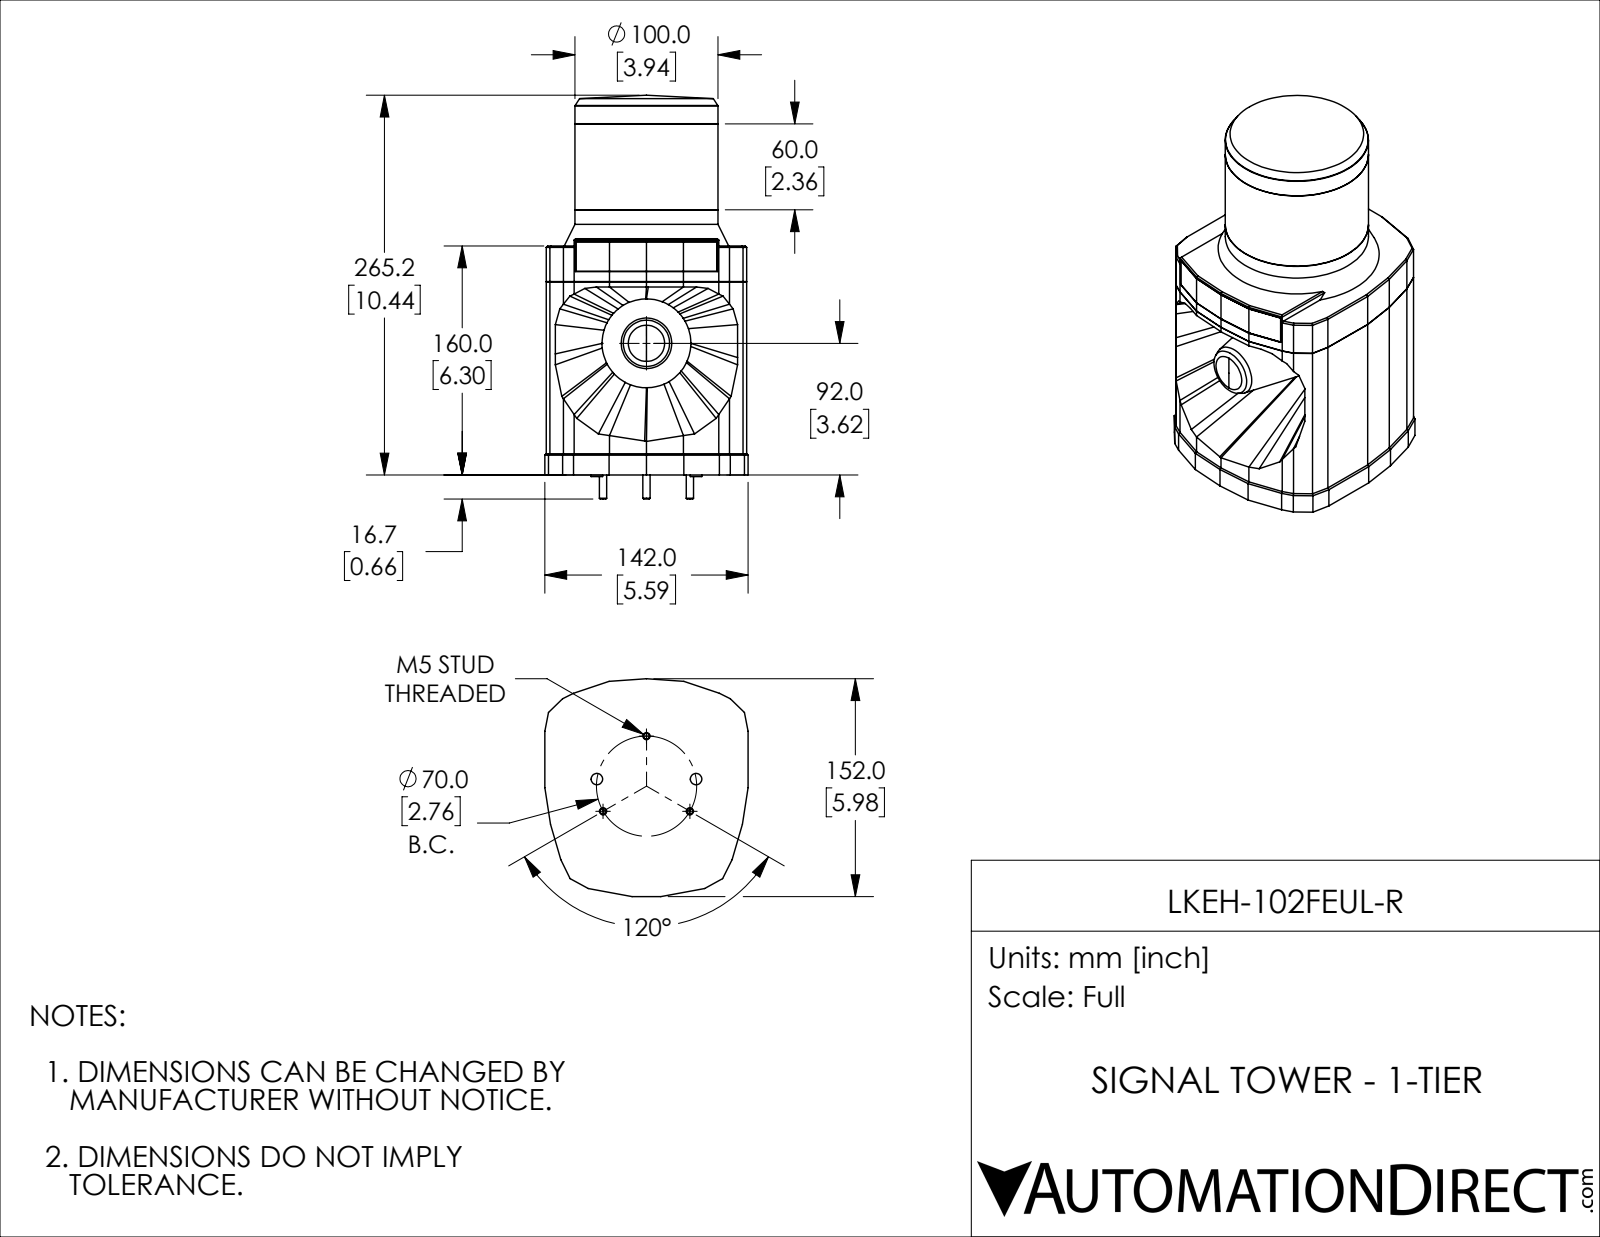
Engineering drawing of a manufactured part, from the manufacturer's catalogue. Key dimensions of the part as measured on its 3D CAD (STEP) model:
Part name (STEP PRODUCT): LKEH-102FEUL-R
STEP written by: SolidWorks 2018 (AUTOMOTIVE_DESIGN)
Units: inches
Bodies: 1 solid, 262 faces (180 planar, 20 cylindrical, 62 other)
Overall size (bounding box): 11.098 × 5.984 × 5.591
Volume: 203 in³ · Surface area: 272.4 in²
Round bosses / shafts (diameter × count): ⌀0.197 ×3, ⌀0.315 ×2, ⌀3.937 ×1, ⌀3.764 ×1
Main face-to-face distances: 0.039, 5.512, 6.299, 6.496, 0.197, 5.551, 1.972, 0.039, 0.04, 9.657
